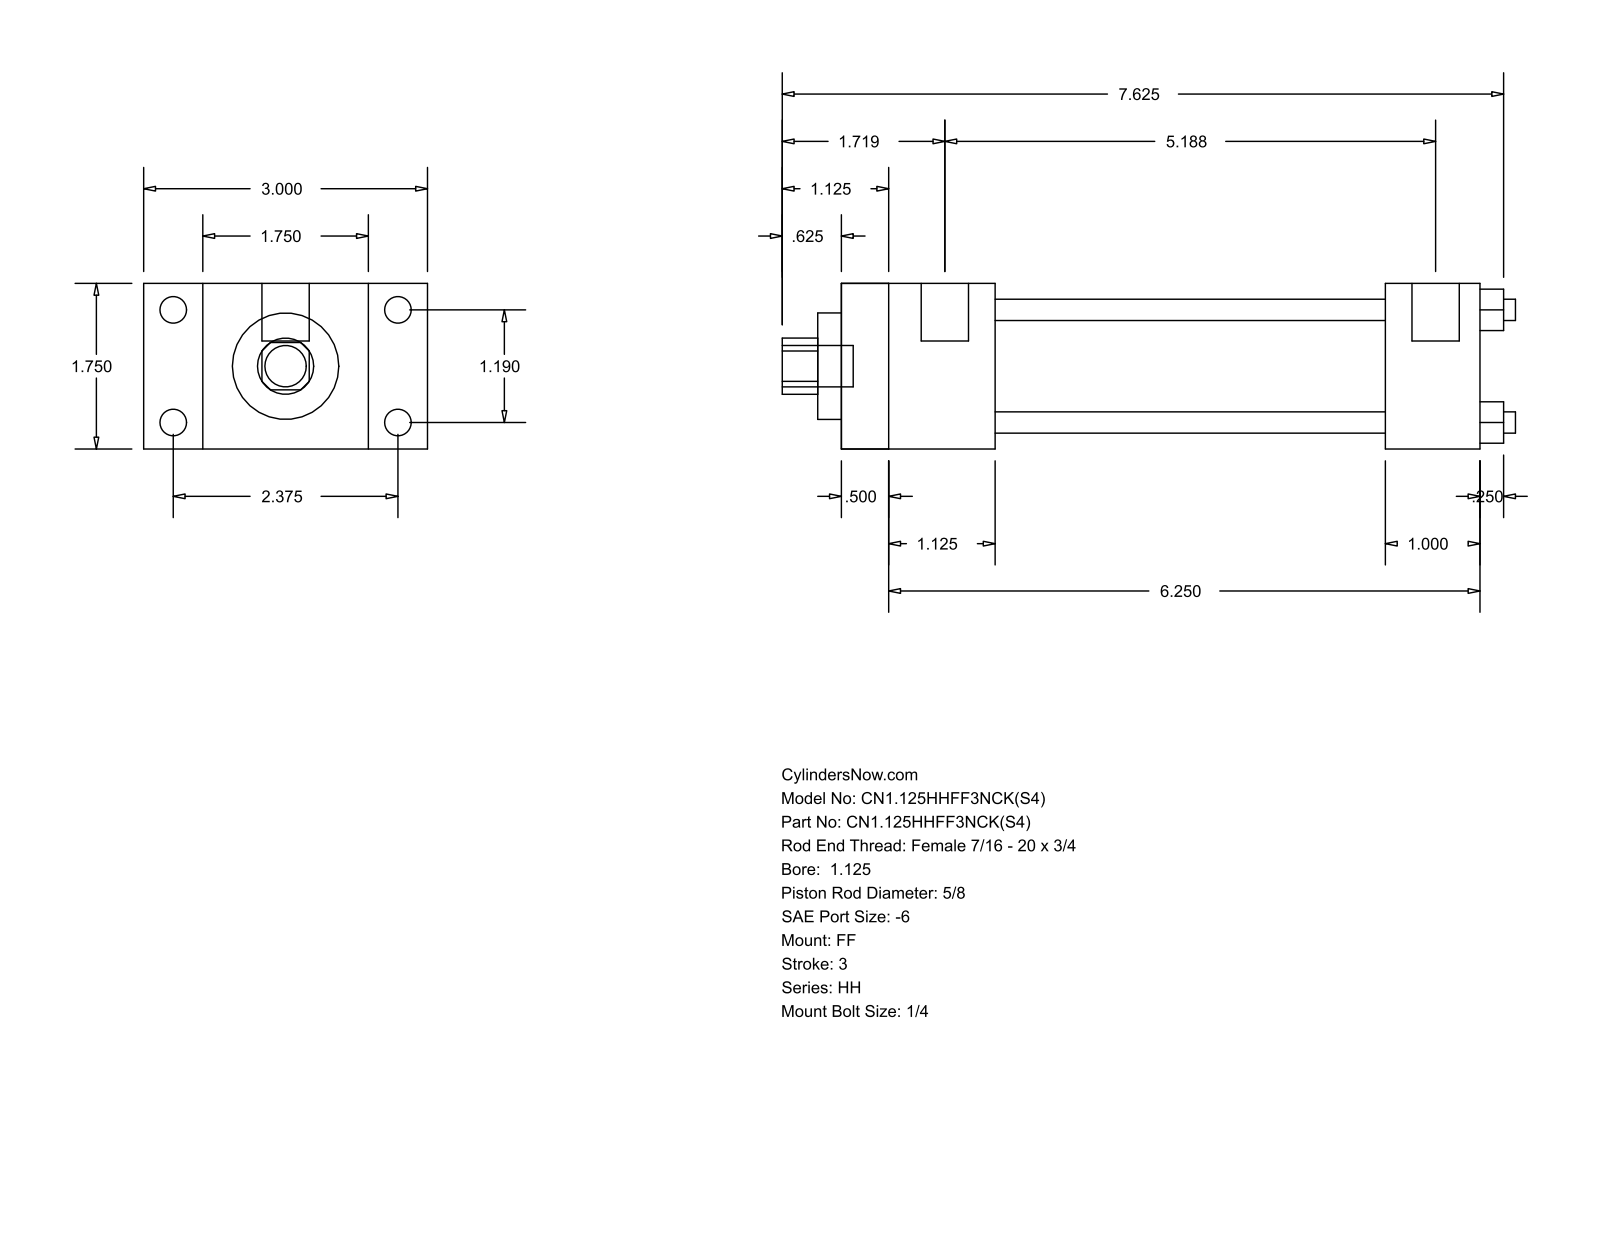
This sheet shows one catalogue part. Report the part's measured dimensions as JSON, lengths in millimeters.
{"part_name": "HH_FF__0112_0.625", "step_written_by": "GSSL Pune (CONFIG_CONTROL_DESIGN)", "units": "millimeters", "bodies": {"solids": 0, "faces": 92, "planar": 64, "cylindrical": 28, "other": 0}, "overall_size": [196.85, 76.2, 44.45], "round_holes": [[5.71, 4], [15.88, 1], [28.57, 1], [34.92, 1]], "round_bosses_or_shafts": [[7.14, 4], [5.56, 4], [12.7, 2], [11.11, 1]], "partial_cylinders_radius": [[7.54, 1]], "face_to_face_distances": [44.46, 171.44, 15.87, 12.69, 158.75, 60.33, 28.58, 41.27, 146.05, 133.36], "hole_center_spacings": [21.37, 30.22, 42.74]}
